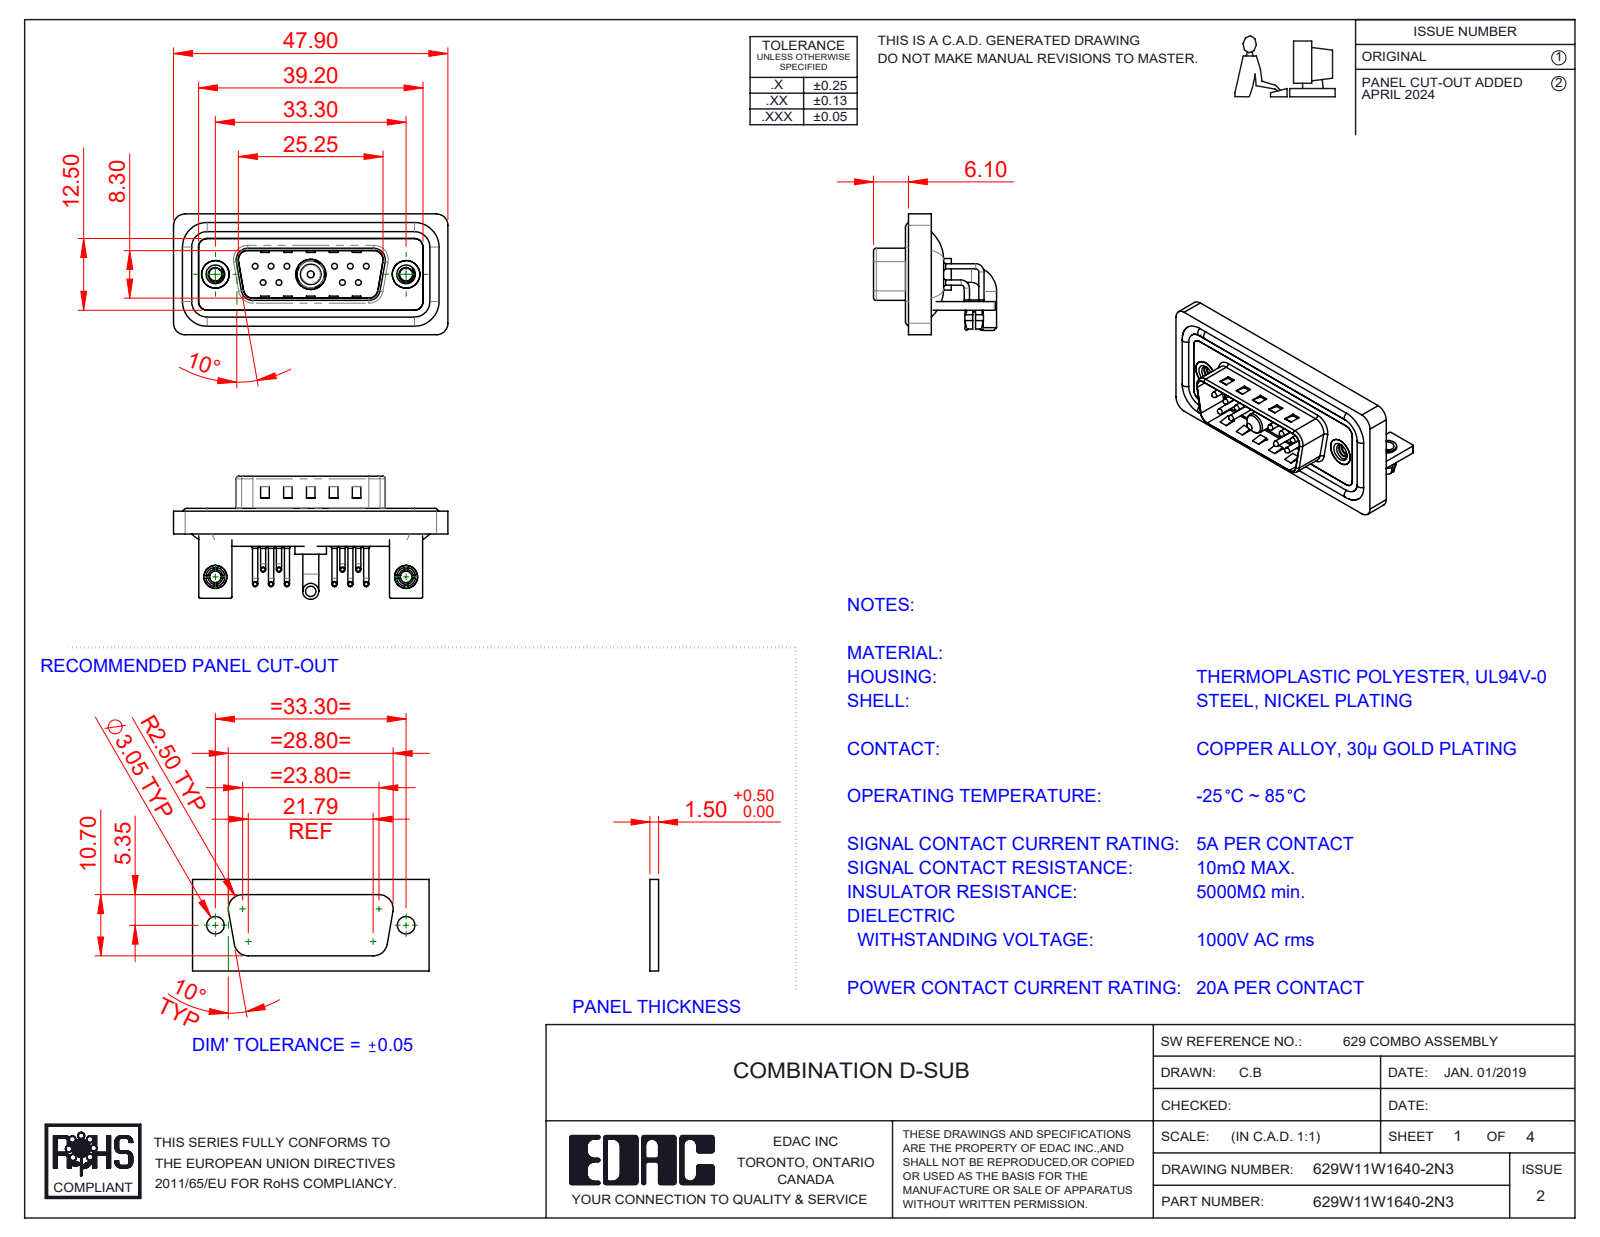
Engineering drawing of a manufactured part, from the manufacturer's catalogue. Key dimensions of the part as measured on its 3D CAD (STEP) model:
Part name (STEP PRODUCT): 629Combo Contact Row 2; Power Pin_20A RA; 629Combo Waterproof Housing_15 Contacts; 629Combo Housing_11W1 (+7 more)
STEP written by: SolidWorks 2023 (CONFIG_CONTROL_DESIGN)
Units: millimetres
Bodies: 23 solids, 1735 faces (904 planar, 619 cylindrical, 212 other)
Overall size (bounding box): 47.9 × 21.5 × 21.1
Volume: 5 903 mm³ · Surface area: 10 077 mm²
Round holes (diameter × count): ⌀2 ×12, ⌀0.75 ×10, ⌀1.6 ×10, ⌀2.26 ×2, ⌀2.5 ×2, ⌀3.2 ×2, ⌀4 ×2, ⌀4.8 ×2, ⌀5 ×2, ⌀4.85 ×1, ⌀5.3 ×1
Round bosses / shafts (diameter × count): ⌀0.9 ×20, ⌀1.5 ×10, ⌀1 ×10, ⌀0.65 ×10, ⌀1.6 ×4, ⌀4.9 ×2, ⌀4 ×2, ⌀3.4 ×2
Partial cylindrical surfaces — rounded edges, fillets, slot ends (radius × count): R2 ×21, R1.5 ×18, R0.25 ×16, R1.01 ×10, R0.5 ×9, R1.6 ×8, R1 ×7, R0.6 ×4
Main face-to-face distances: 0.4, 0.8, 1.5, 2.9, 2.1, 1.1, 1.6, 1.2, 3.7, 4.1
Hole centre spacings: 3.16, 2.77, 13.85, 11.08, 16.62, 5.03, 5.04, 5.54
